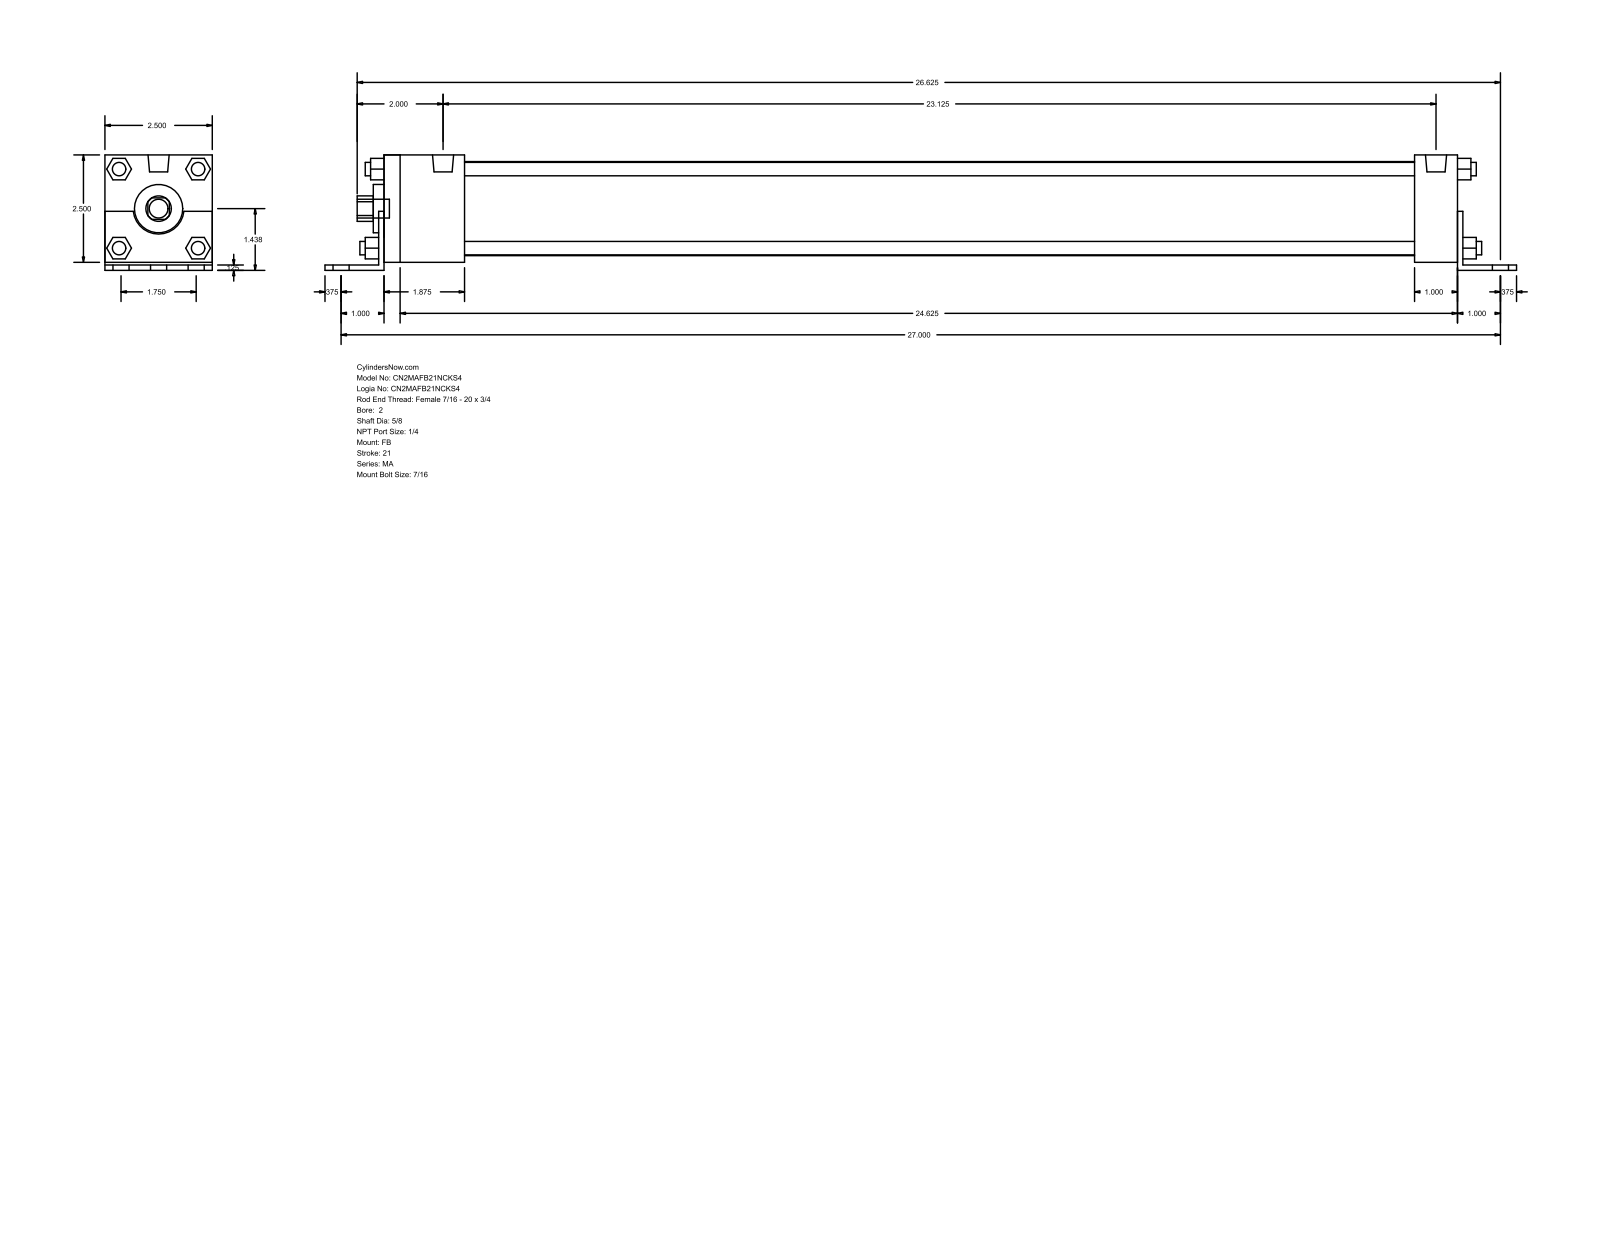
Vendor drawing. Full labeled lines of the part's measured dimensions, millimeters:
Part name (STEP PRODUCT): MA_FB__0200_0.625
STEP written by: GSSL Pune (CONFIG_CONTROL_DESIGN)
Units: millimetres
Bodies: 0 solids, 140 faces (105 planar, 35 cylindrical, 0 other)
Overall size (bounding box): 704.85 × 68.26 × 63.5
Round holes (diameter × count): ⌀15.88 ×1, ⌀28.57 ×1, ⌀55.63 ×1
Round bosses / shafts (diameter × count): ⌀7.94 ×8, ⌀11.11 ×7, ⌀12.49 ×2
Partial cylindrical surfaces — rounded edges, fillets, slot ends (radius × count): R7.54 ×1, R15.05 ×1
Main face-to-face distances: 63.5, 3.17, 4.76, 68.26, 1.59, 65.09, 635, 641.35, 3.18, 638.17
